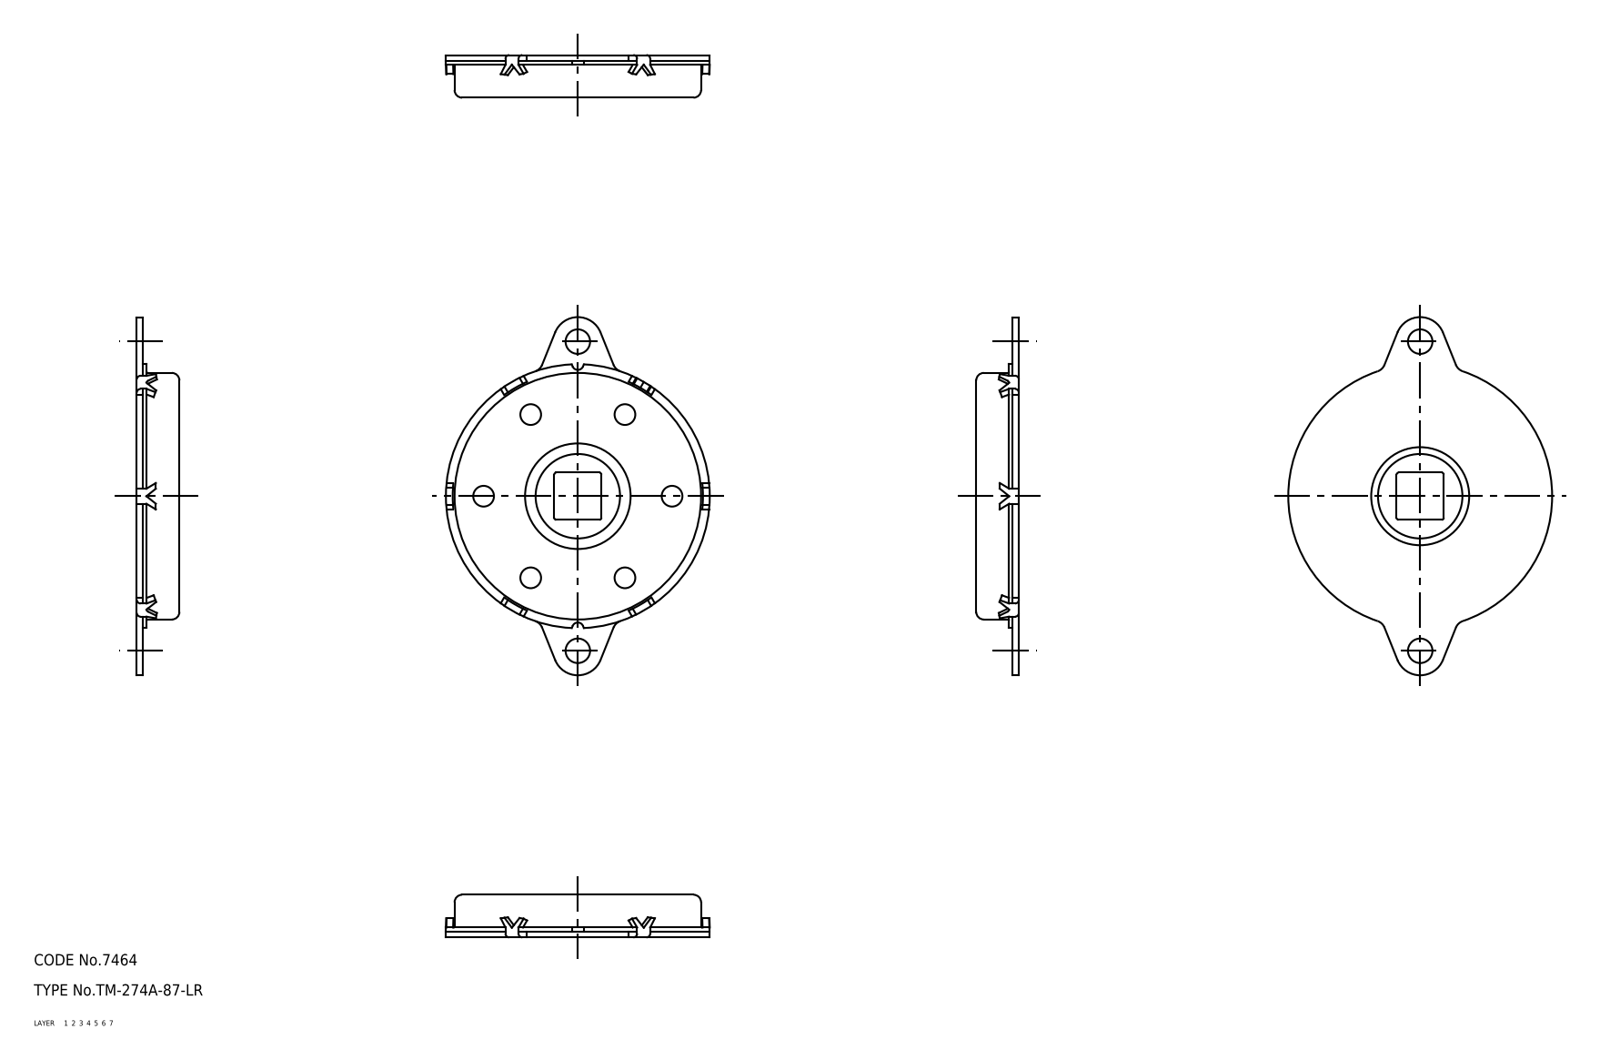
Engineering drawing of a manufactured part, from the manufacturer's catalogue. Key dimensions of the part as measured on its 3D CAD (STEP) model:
Part name (STEP PRODUCT): inner ring; TM_274A_87_LR_662_36
STEP written by: CADfix (AUTOMOTIVE_DESIGN)
Units: millimetres
Bodies: 2 solids, 203 faces (0 planar, 0 cylindrical, 203 other)
Overall size (bounding box): 95 × 70 × 11.3
Volume: 36 597 mm³ · Surface area: 13 313 mm²
